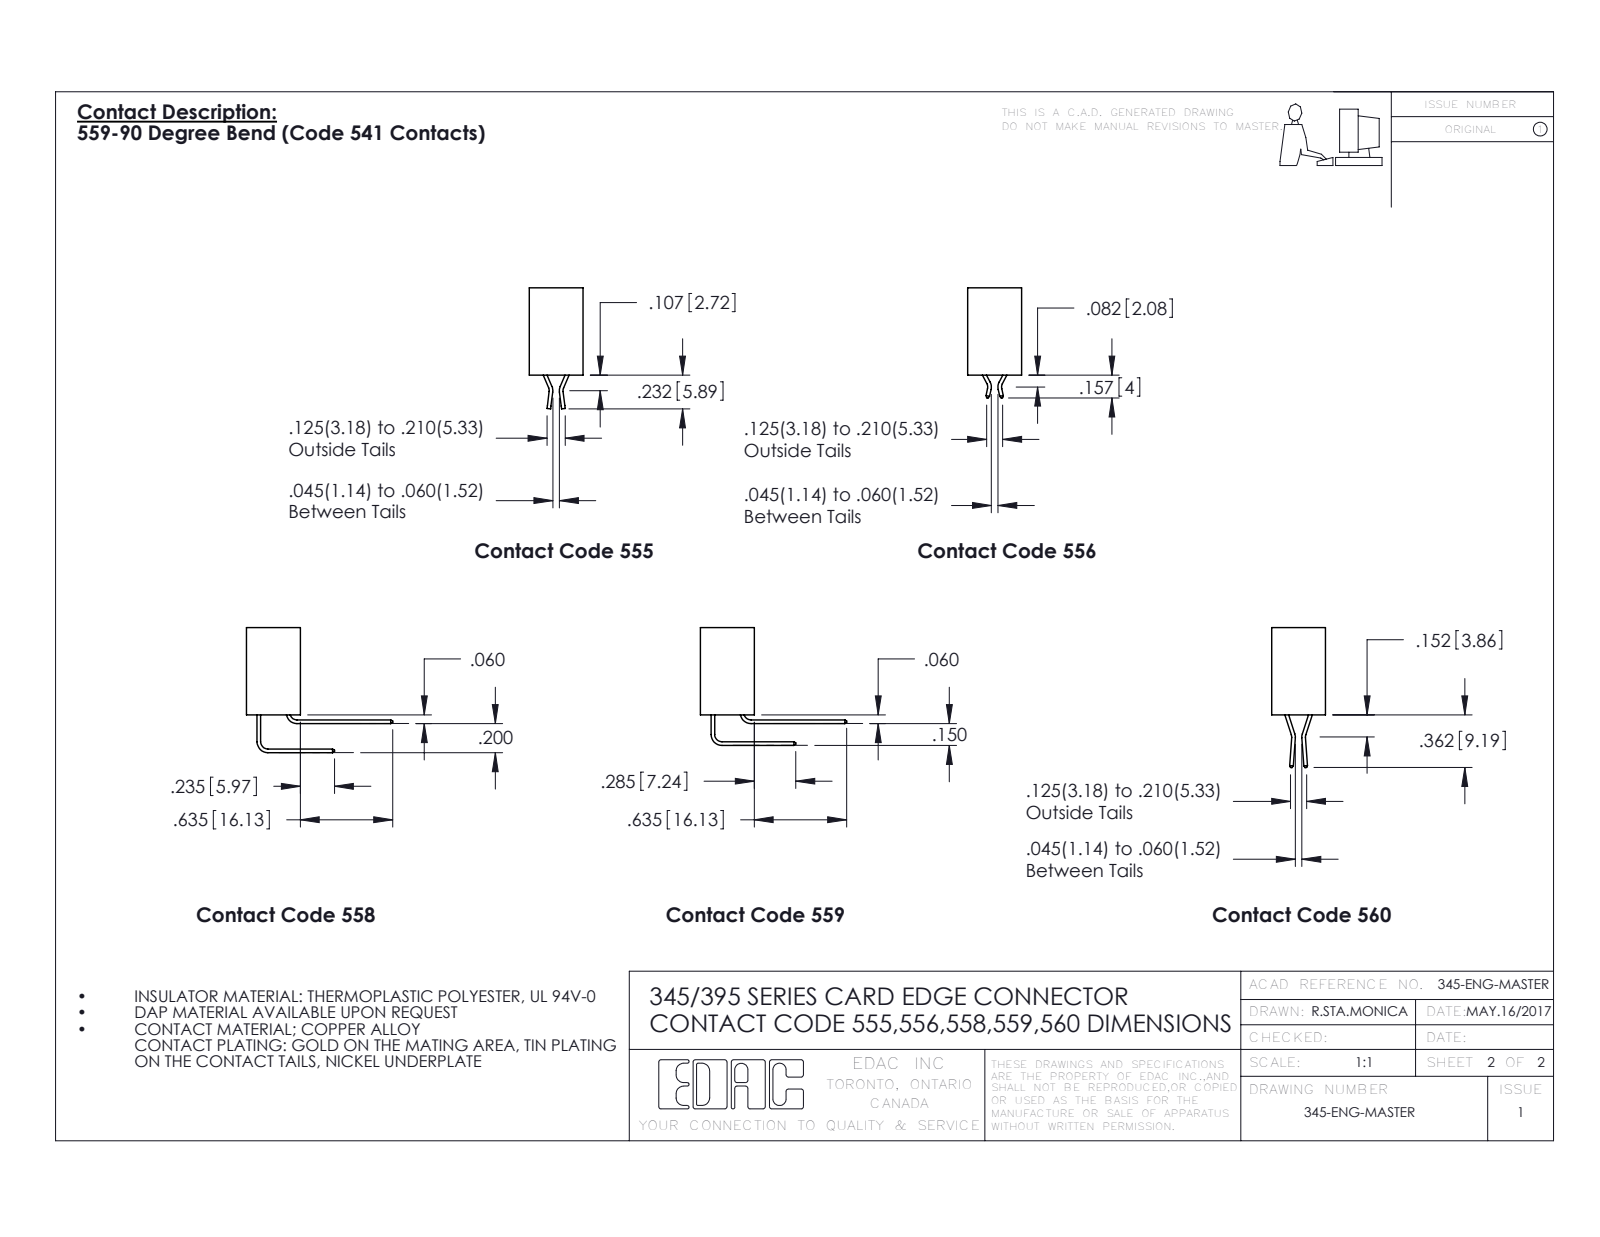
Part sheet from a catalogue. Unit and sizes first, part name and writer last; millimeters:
Units: millimetres
Overall size (bounding box): 204.1 × 25.5 × 21.8
Round holes (diameter × count): ⌀3.3 ×2, ⌀1.6 ×1
Partial cylindrical surfaces — rounded edges, fillets, slot ends (radius × count): R0.2 ×216, R0.3 ×22, R0.2 ×6, R0.8 ×6, R0.7 ×3, R0.4 ×2, R0.5 ×2, R0.6 ×2
Main face-to-face distances: 1.8, 7.6, 5.1, 9.4, 2.5, 6.9, 0.6, 5.7, 0.6, 4.4
Hole centre spacings: 197.5
Volume: 20 840 mm³ · Surface area: 35 170 mm²
Bodies: 145 solids, 7614 faces (5120 planar, 2494 cylindrical, 0 other)
Part name (STEP PRODUCT): 345 Part_Flush Mounting Lugs - Side Mount; 345-292-001_558 559 Tail - 1; 395-144-558-212; 345-292-001_558 Tail - 2
STEP written by: SolidWorks 2016 (CONFIG_CONTROL_DESIGN)
